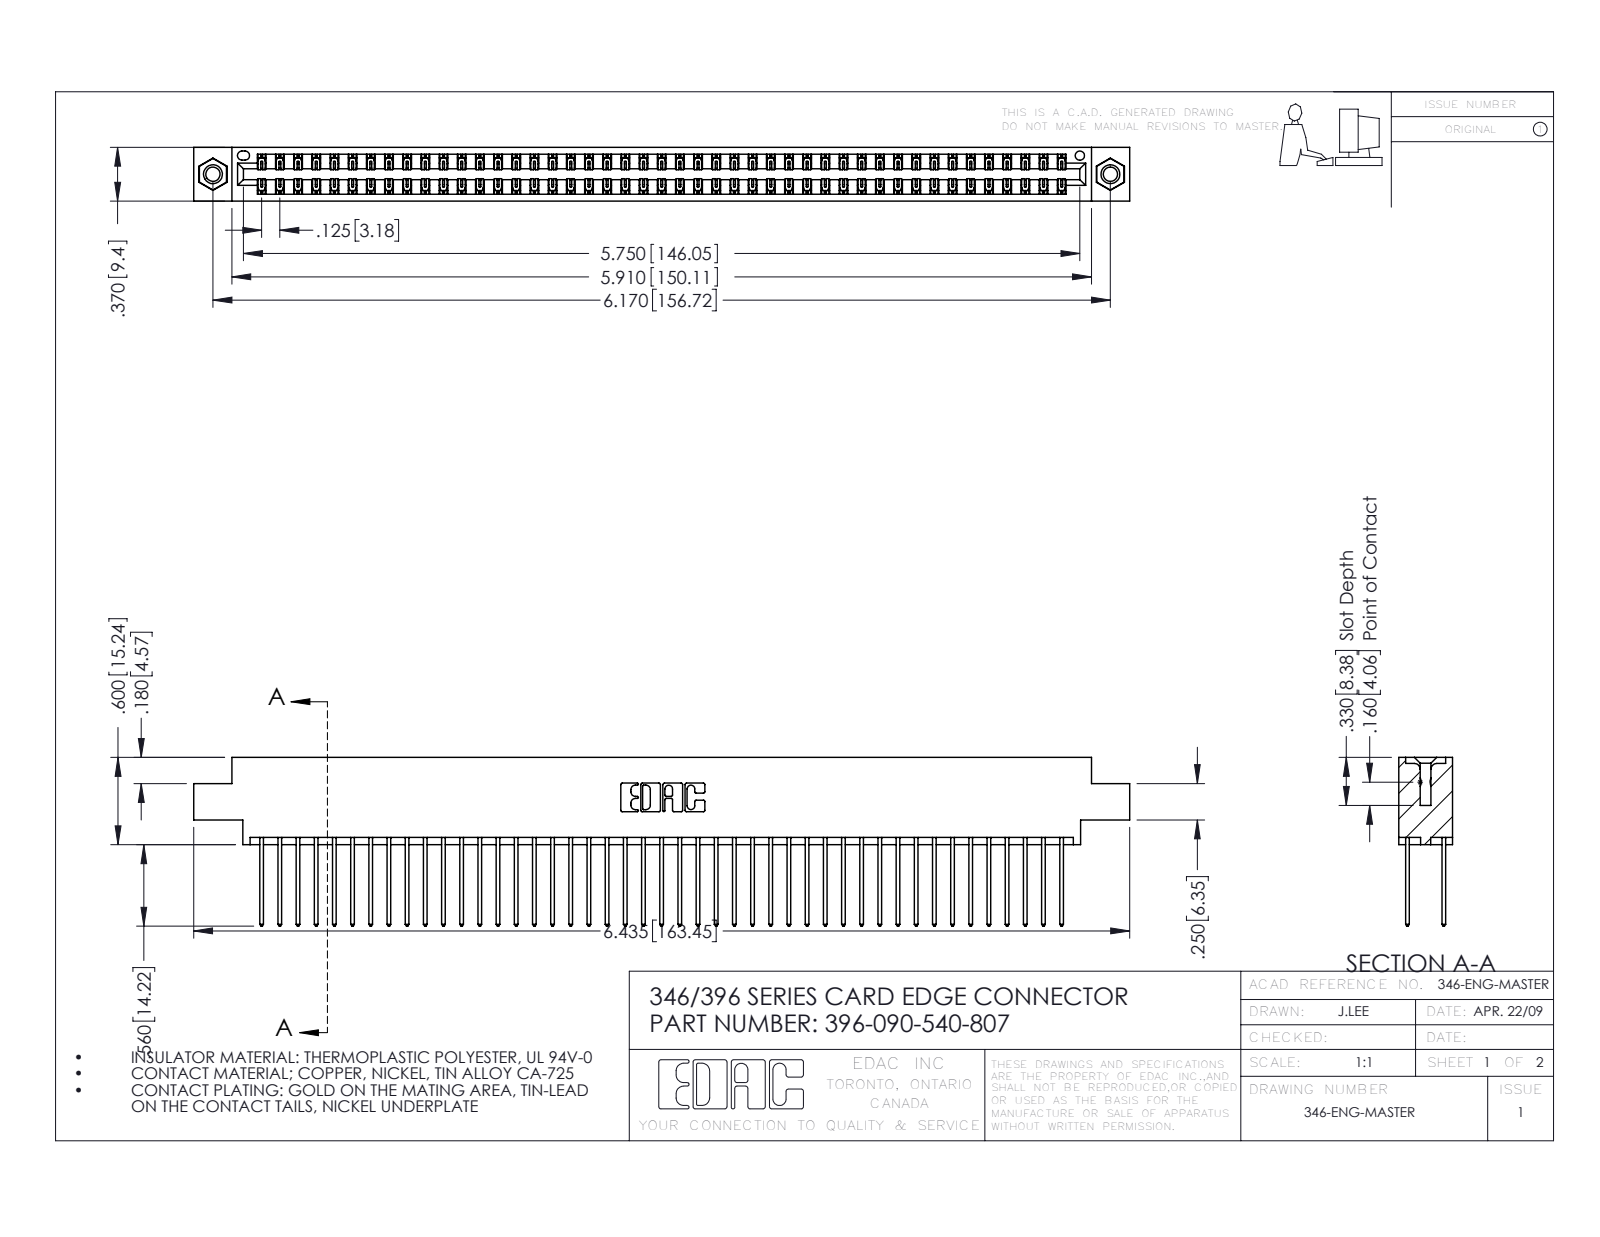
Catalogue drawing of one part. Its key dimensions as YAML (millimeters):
part_name: "345-250-001_345-250-005-103; 396-090-540-807; 345-292-001_345-293-140; 346 Part_0.170 Offset - 0.156 Dia-TI"
step_written_by: "SolidWorks 2016 (CONFIG_CONTROL_DESIGN)"
units: millimeters
bodies: {solids: 93, faces: 4866, planar: 3262, cylindrical: 1588, other: 16}
overall_size: [163.4, 29.5, 9.4]
volume: 16100
surface_area: 24050
round_holes:
  - {diameter: 2.5, count: 2}
  - {diameter: 3.2, count: 2}
  - {diameter: 4, count: 2}
  - {diameter: 1.6, count: 1}
round_bosses_or_shafts:
  - {diameter: 3.9, count: 2}
partial_cylinders:
  - {radius: 0.2, count: 135}
  - {radius: 0.3, count: 90}
  - {radius: 0.3, count: 22}
  - {radius: 0.2, count: 6}
  - {radius: 0.8, count: 6}
  - {radius: 0.7, count: 3}
  - {radius: 0.4, count: 2}
  - {radius: 0.6, count: 2}
face_to_face_distances: [1.2, 8.2, 6.4, 1.8, 7.6, 0.6, 9.4, 7, 5.6, 3.8]
hole_center_spacings: [6.2, 151.4, 156.7]
